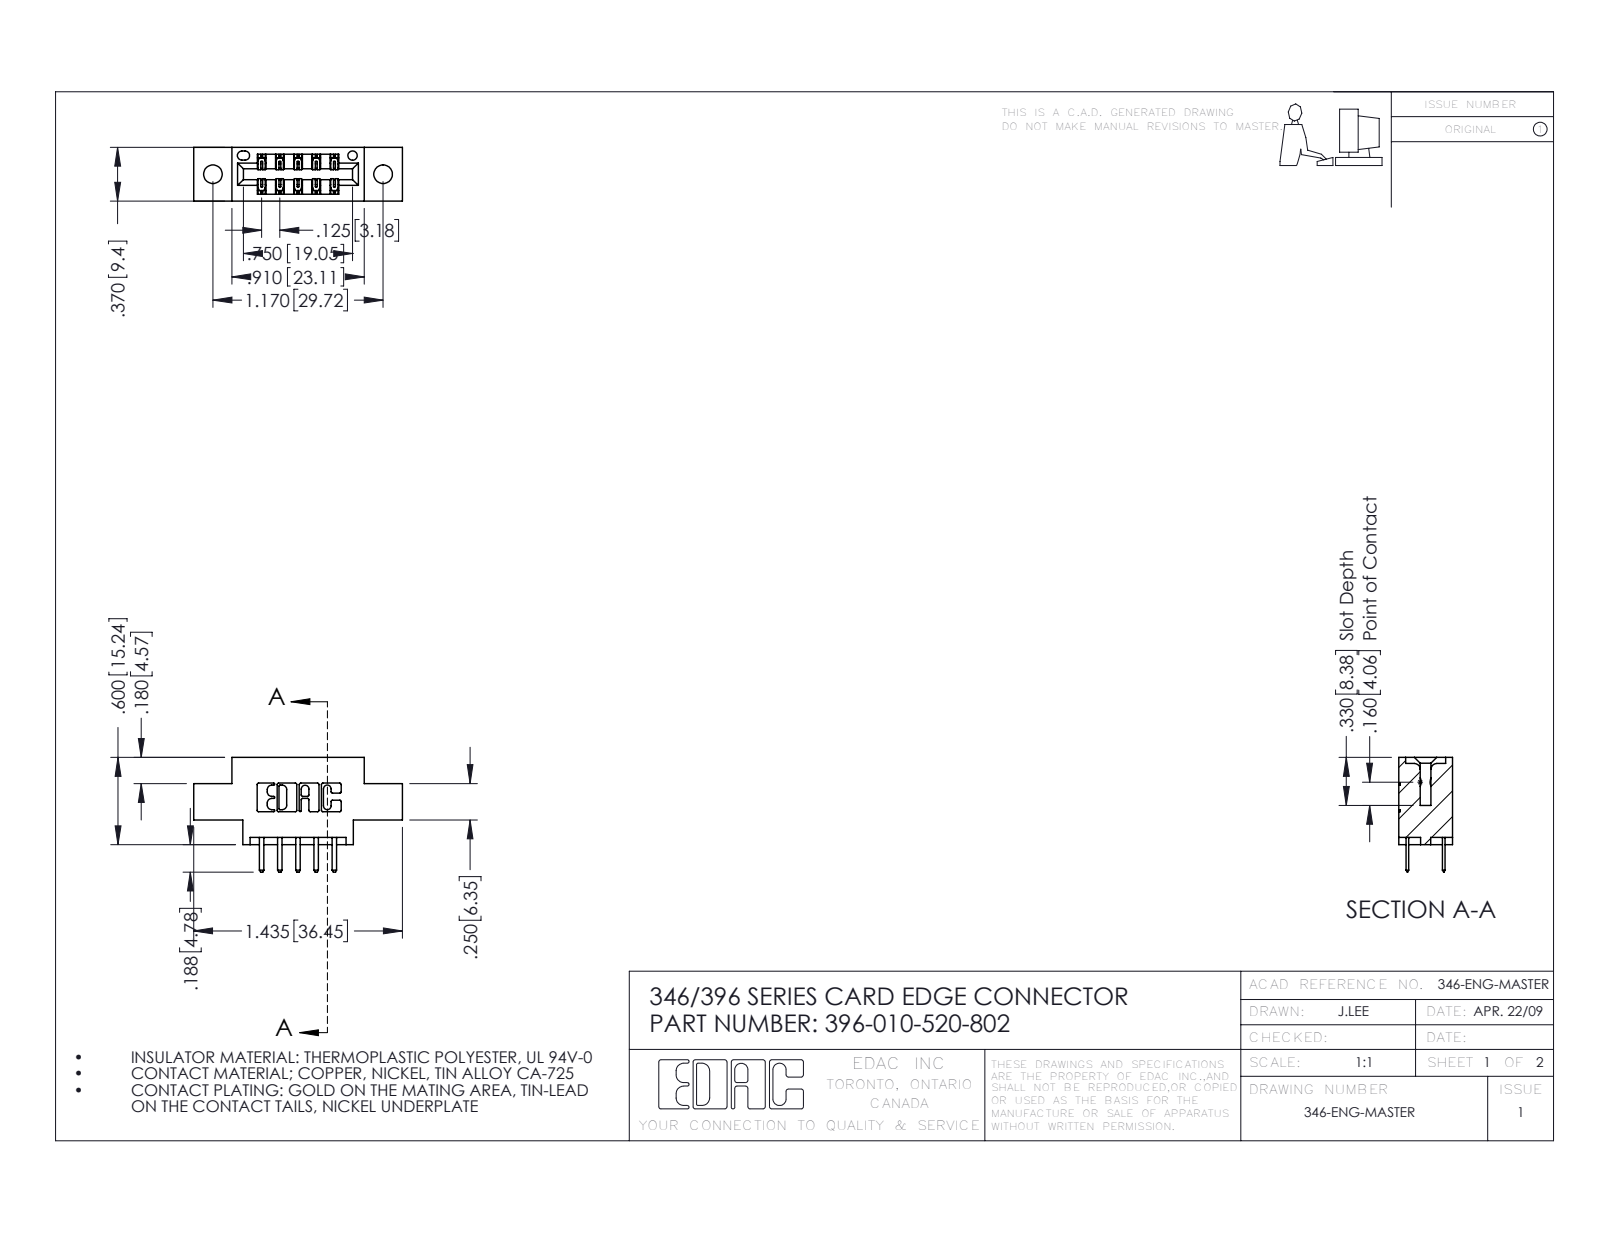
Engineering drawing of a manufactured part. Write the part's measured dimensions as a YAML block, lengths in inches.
part_name: "345-292-001_345-293-120; 346 Part_0.170 Offset - 0.128 Dia; 396-010-520-802"
step_written_by: "SolidWorks 2016 (CONFIG_CONTROL_DESIGN)"
units: inches
bodies: {solids: 11, faces: 686, planar: 450, cylindrical: 236, other: 0}
overall_size: [1.435, 0.788, 0.37]
volume: 0.187
surface_area: 5.487
round_holes:
  - {diameter: 0.128, count: 2}
  - {diameter: 0.064, count: 1}
partial_cylinders:
  - {radius: 0.01, count: 22}
  - {radius: 0.006, count: 15}
  - {radius: 0.01, count: 14}
  - {radius: 0.007, count: 6}
  - {radius: 0.031, count: 6}
  - {radius: 0.026, count: 3}
  - {radius: 0.014, count: 2}
  - {radius: 0.022, count: 2}
face_to_face_distances: [0.25, 0.37, 0.048, 0.322, 0.148, 0.222, 0.1, 0.174, 0.55, 0.072]
hole_center_spacings: [0.246, 0.969, 1.17]
